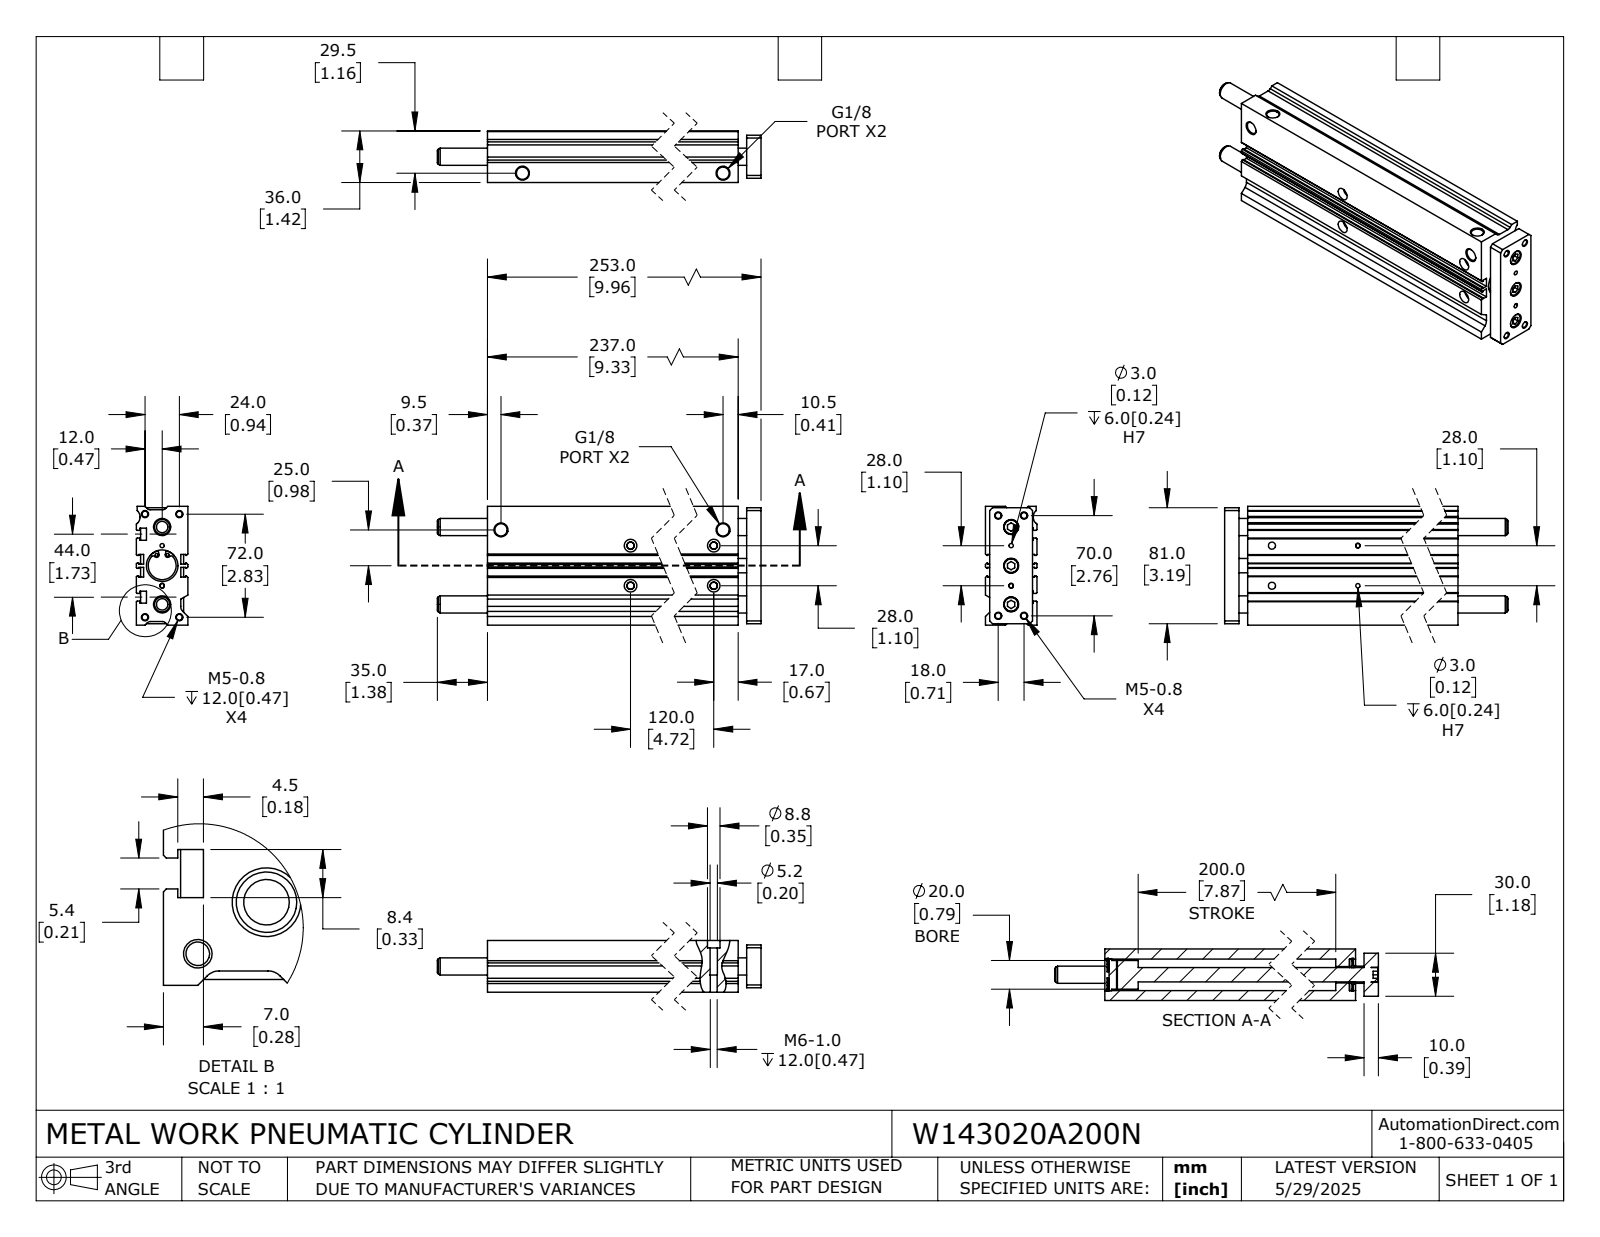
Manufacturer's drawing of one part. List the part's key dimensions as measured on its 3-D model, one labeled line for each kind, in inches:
Part name (STEP PRODUCT): W143020A200N_BODY; W143020A200N; W143020A200N_ROD
STEP written by: SolidWorks 2024 (CONFIG_CONTROL_DESIGN)
Units: inches
Bodies: 6 solids, 357 faces (174 planar, 145 cylindrical, 38 other)
Overall size (bounding box): 11.339 × 3.268 × 1.417
Volume: 35.59 in³ · Surface area: 251.6 in²
Round holes (diameter × count): ⌀0.163 ×8, ⌀0.079 ×4, ⌀0.118 ×4, ⌀0.205 ×4, ⌀0.337 ×4, ⌀0.346 ×4, ⌀0.413 ×3, ⌀0.194 ×2, ⌀0.194 ×2, ⌀0.472 ×2, ⌀0.449 ×1, ⌀0.767 ×1
Round bosses / shafts (diameter × count): ⌀0.394 ×3, ⌀0.906 ×2, ⌀0.787 ×1, ⌀0.512 ×1
Partial cylindrical surfaces — rounded edges, fillets, slot ends (radius × count): R0.053 ×4, R0.059 ×4, R0.071 ×4, R0.118 ×4, R0.197 ×3
Main face-to-face distances: 1.417, 0.098, 0.197, 1.22, 0.079, 3.268, 0.276, 3.169, 1.024, 0.945
Hole centre spacings: 0.124, 0.296, 0.336, 0.474, 0.591, 0.78, 0.828, 0.864
